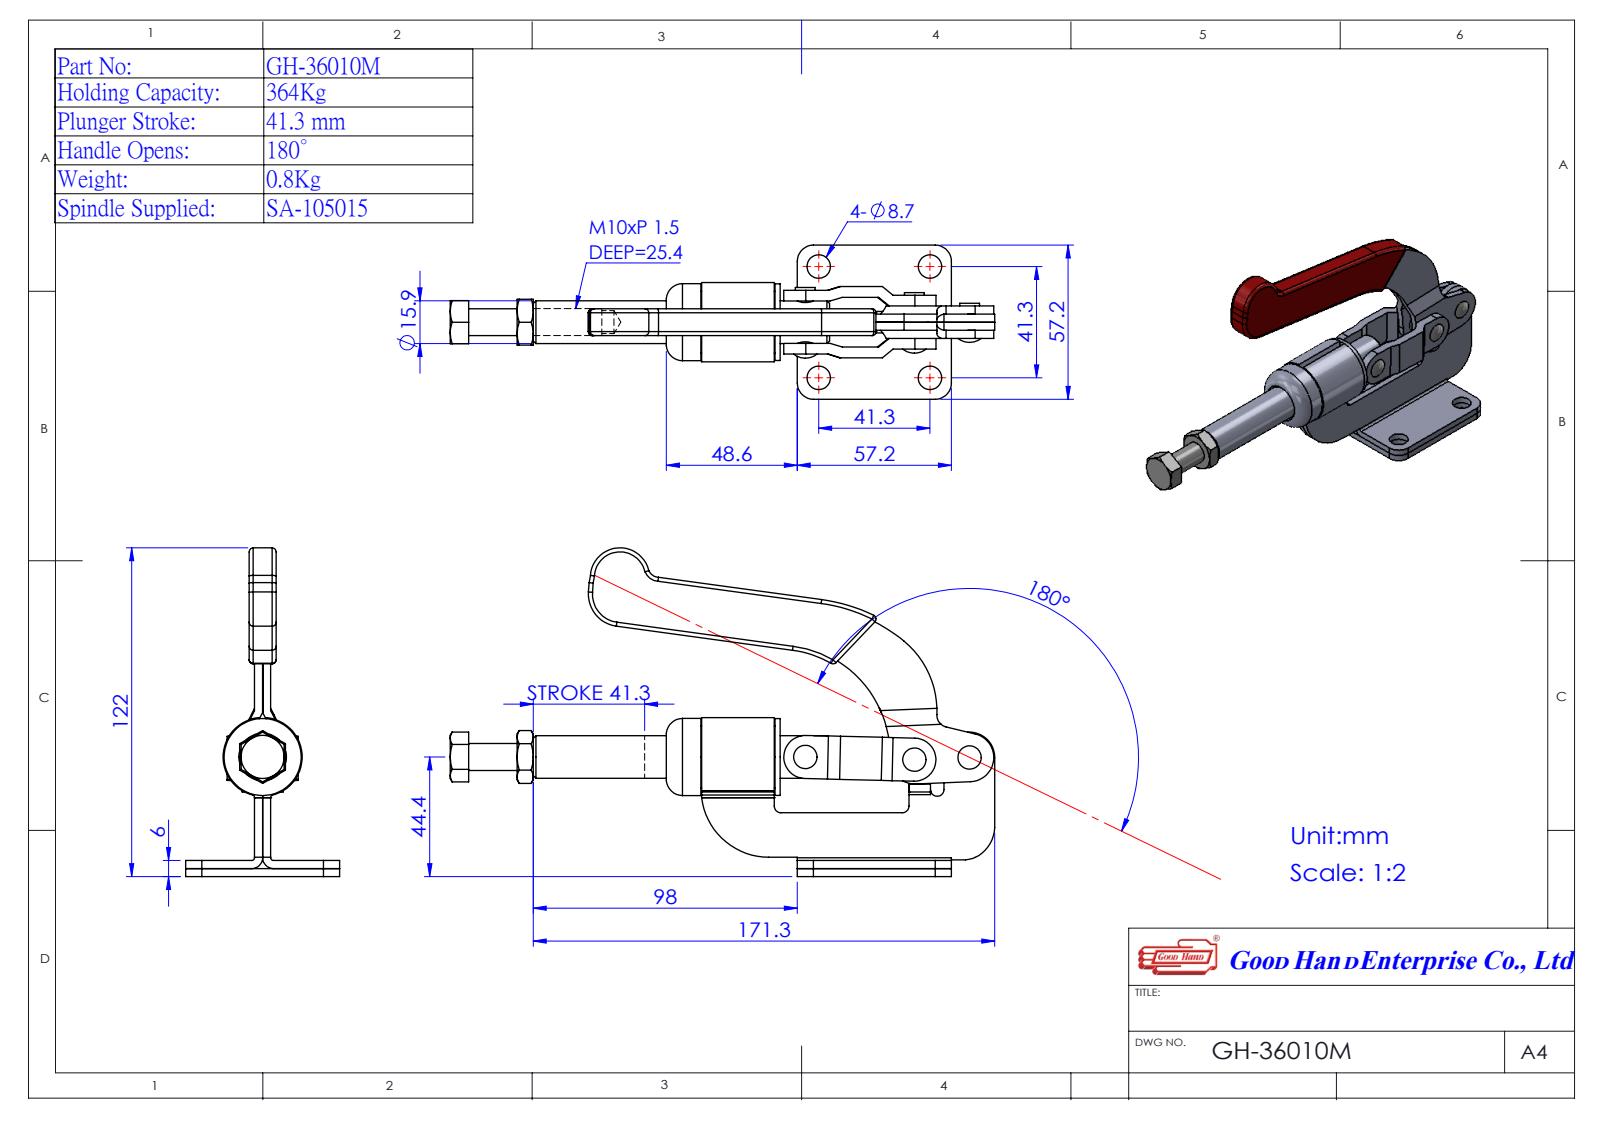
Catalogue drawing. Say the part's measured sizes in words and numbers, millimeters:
The part is named "GH-36010M(簡化); 436010M33-1^GH-36010M(簡化); Group5^GH-36010M(簡化); Group3^GH-36010M(簡化) (+2 more)". Its 3-D file was written by "SolidWorks 2016 (AUTOMOTIVE_DESIGN)". It is 6 solids with 297 faces: 131 planar, 124 cylindrical and 42 other. Overall it measures 202.15 by 122 by 57.2 millimeters. Its volume is 109 280 cubic millimeters and its surface area 56 187 square millimeters. Round holes: 4 of diameter 8.7, 4 of diameter 9.2, 3 of diameter 4.5, 1 of diameter 8.5, 1 of diameter 10, 1 of diameter 15.85, 1 of diameter 23.2. Round bosses or shafts: 2 of diameter 5.5, 1 of diameter 28.6, 1 of diameter 28.5, 1 of diameter 23, 1 of diameter 6. Partial cylindrical surfaces (rounded edges, fillets, slot ends): 6 of radius 1, 4 of radius 4, 4 of radius 6, 3 of radius 2.5, 2 of radius 8, 2 of radius 12, 1 of radius 4.27, 1 of radius 4.5. The main face-to-face distances are 6, 3, 2, 8, 5, 10, 11, 1, 9, 4. The hole center spacings are 41.3, 58.41, 20.5, 40.5, 60.97.
